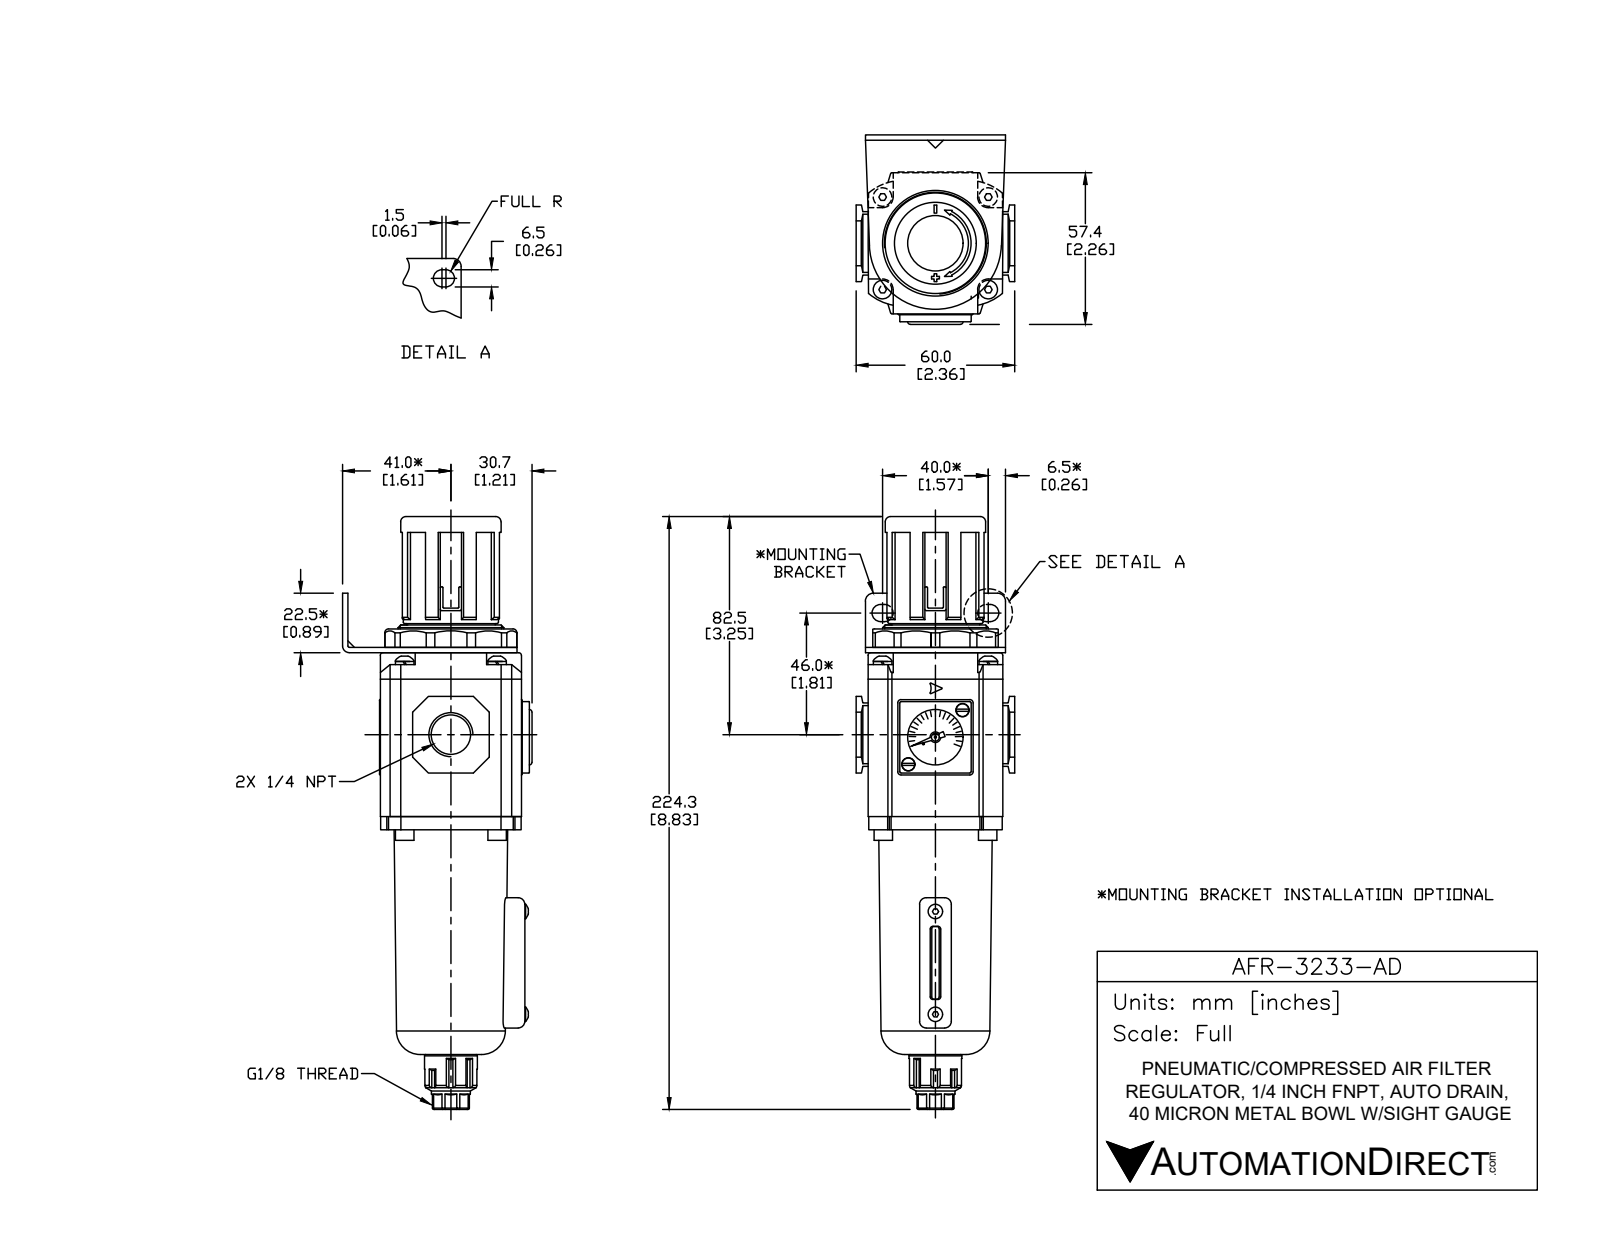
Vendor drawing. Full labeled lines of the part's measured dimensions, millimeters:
Part name (STEP PRODUCT): AFR-3233-AD
STEP written by: SolidWorks 2015 (CONFIG_CONTROL_DESIGN)
Units: millimetres
Bodies: 16 solids, 686 faces (418 planar, 181 cylindrical, 87 other)
Overall size (bounding box): 224.3 × 72 × 60
Volume: 361 874 mm³ · Surface area: 64 386 mm²
Round holes (diameter × count): ⌀3 ×6, ⌀2 ×1, ⌀6.2 ×1, ⌀11.13 ×1, ⌀21 ×1, ⌀30 ×1, ⌀32 ×1
Round bosses / shafts (diameter × count): ⌀5.5 ×6, ⌀7 ×4, ⌀2.7 ×2, ⌀40 ×1, ⌀38 ×1, ⌀36 ×1, ⌀33.5 ×1, ⌀20.46 ×1
Partial cylindrical surfaces — rounded edges, fillets, slot ends (radius × count): R1 ×16, R1.2 ×10, R1.3 ×8, R2.5 ×8, R9.5 ×8, R19.9 ×8, R0.5 ×6, R3.25 ×6
Main face-to-face distances: 2, 62, 64, 53.4, 51, 1, 55.5, 52.4, 4.5, 67
Hole centre spacings: 26.58, 14.5, 35, 40, 53.15, 28.99
